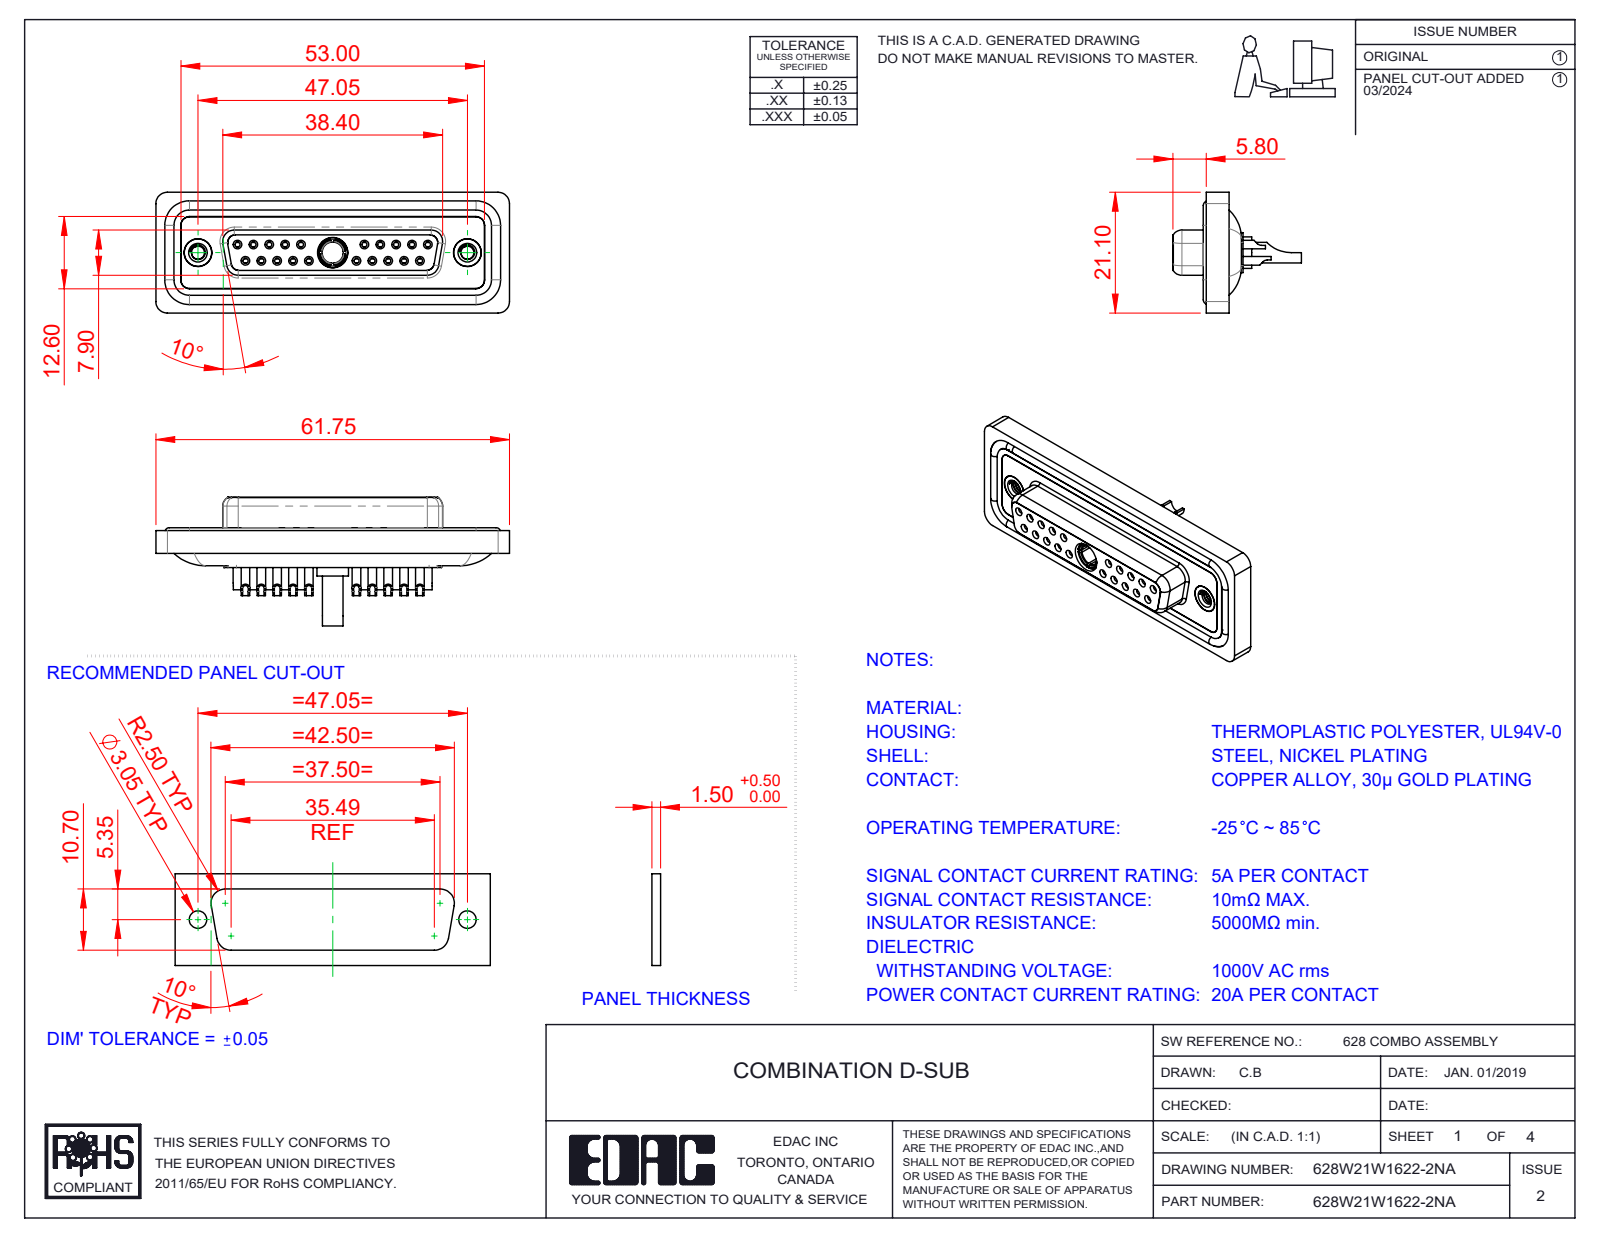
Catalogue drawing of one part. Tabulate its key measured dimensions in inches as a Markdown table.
| quantity | value |
| --- | --- |
| part name | 628W21W1622-2NA; 628Combo Contact Row 2_22; 628Combo Threaded Rivet_A; 628Combo Contact Row 1_22 (+5 more) |
| STEP written by | SolidWorks 2023 (CONFIG_CONTROL_DESIGN) |
| units | inches |
| bodies | 29 solids, 1564 faces (477 planar, 636 cylindrical, 451 other) |
| overall size | 2.431 × 0.884 × 0.831 |
| volume | 0.514 in³ |
| surface area | 22.15 in² |
| round holes (diameter × count) | 0.035 × 20, 0.039 × 20, 0.043 × 20, 0.059 × 20, 0.079 × 20, 0.063 × 10, 0.067 × 10, 0.191 × 3, 0.089 × 2, 0.157 × 2, 0.159 × 2, 0.197 × 2 |
| round bosses / shafts (diameter × count) | 0.087 × 20, 0.063 × 14, 0.195 × 2, 0.189 × 2, 0.217 × 1, 0.205 × 1, 0.195 × 1, 0.187 × 1 |
| partial cylindrical surfaces (radius × count) | 0.059 × 22, 0.079 × 18, 0.053 × 8, 0.063 × 8, 0.039 × 6, 0.01 × 4, 0.02 × 4, 0.024 × 4 |
| main face-to-face distances | 0.016, 0.071, 0.293, 0.222, 0.26, 0.02, 0.063, 0.278, 0.114, 0.043 |
| hole center spacings | 0.124, 0.109, 0.218, 0.198, 0.327, 0.294, 0.654, 0.763 |
